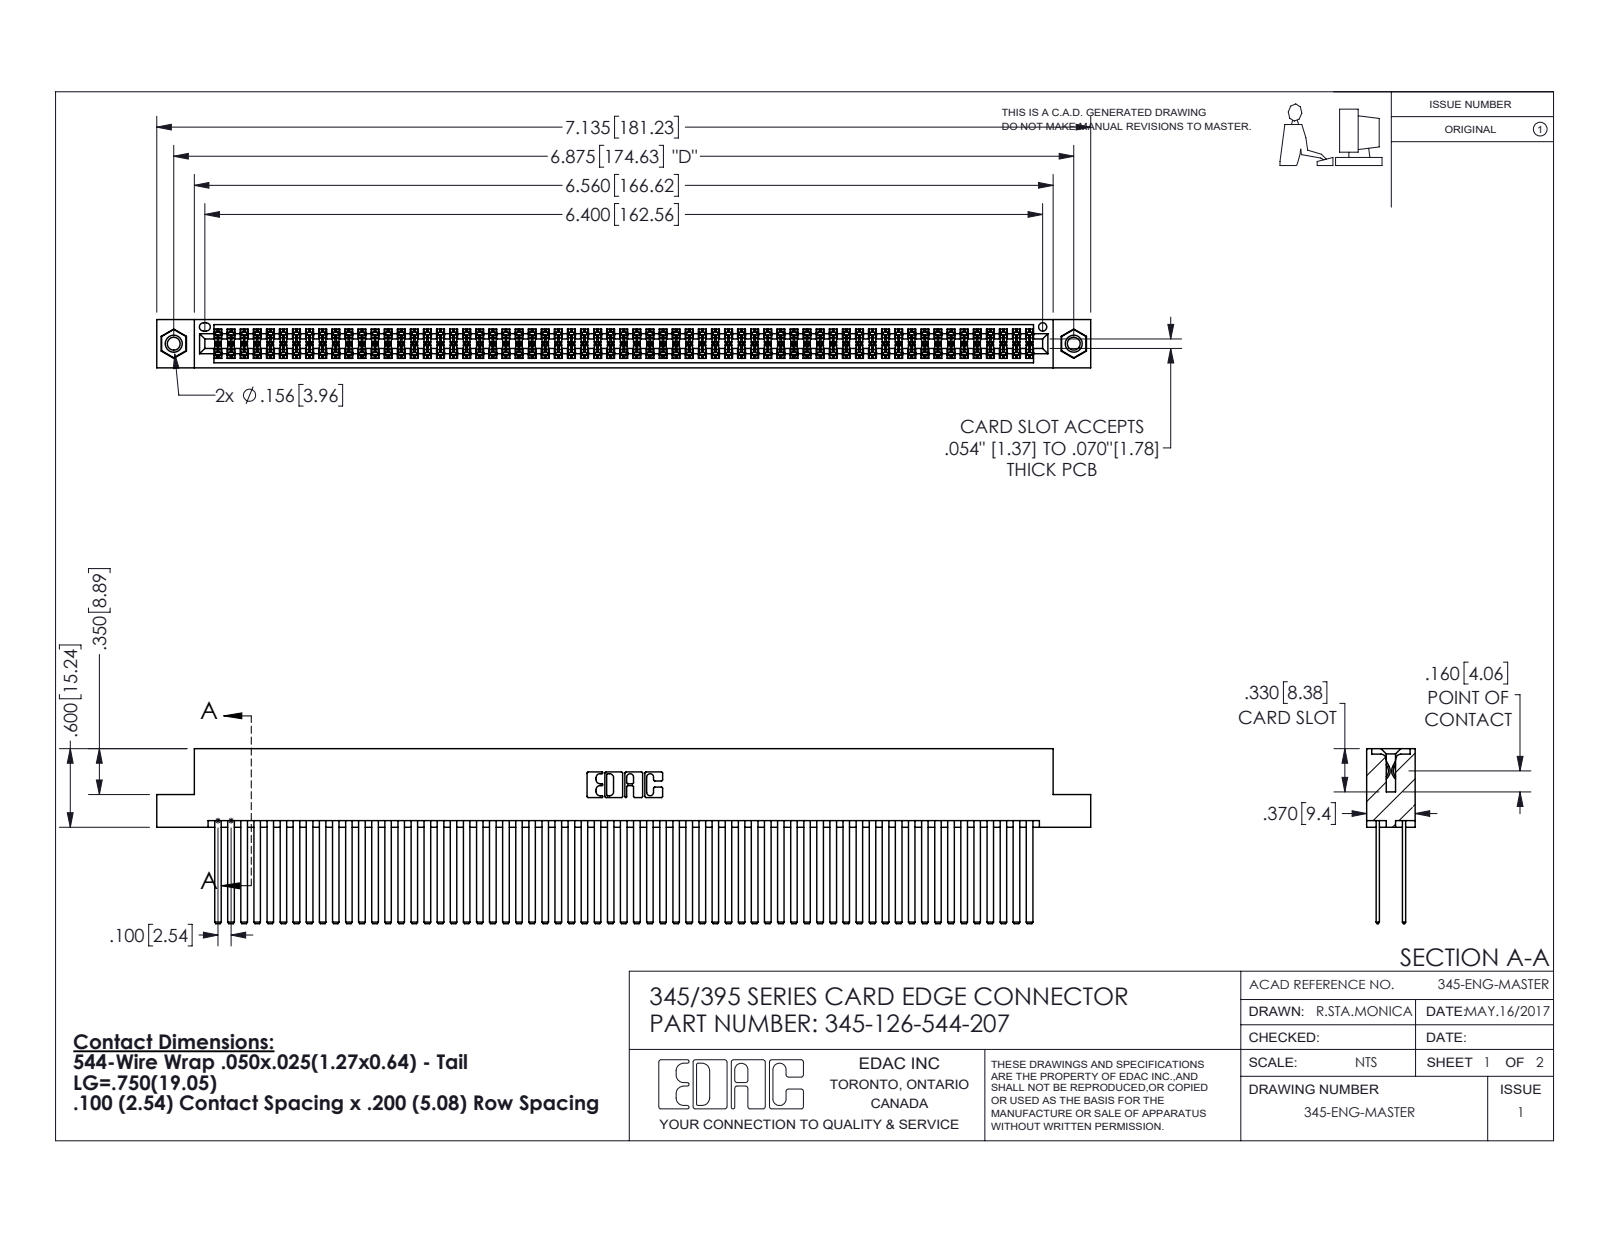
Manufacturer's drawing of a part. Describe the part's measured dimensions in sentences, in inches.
The part is named "345 Part_Flush Mounting Lugs - 0.156 Dia-TI; 345-250-001_345-250-005-103; 345-126-544-207; 345-292-001_345-293-144". Its 3-D file was written by "SolidWorks 2016 (CONFIG_CONTROL_DESIGN)". It is 129 solids with 5730 faces: 3766 planar, 1948 cylindrical and 16 other. Overall it measures 7.135 by 1.337 by 0.37 inches. Its volume is 1.193 cubic inches and its surface area 53.5 square inches. Round holes: 2 of diameter 0.098, 2 of diameter 0.125, 2 of diameter 0.156, 1 of diameter 0.064. Round bosses or shafts: 2 of diameter 0.155. Partial cylindrical surfaces (rounded edges, fillets, slot ends): 189 of radius 0.006, 22 of radius 0.01, 6 of radius 0.007, 6 of radius 0.031, 3 of radius 0.026, 2 of radius 0.014, 2 of radius 0.019, 2 of radius 0.022. The main face-to-face distances are 0.2, 0.025, 0.072, 0.098, 0.272, 0.298, 0.225, 0.175, 0.37, 0.05. The hole center spacings are 0.27, 6.639, 6.875.
